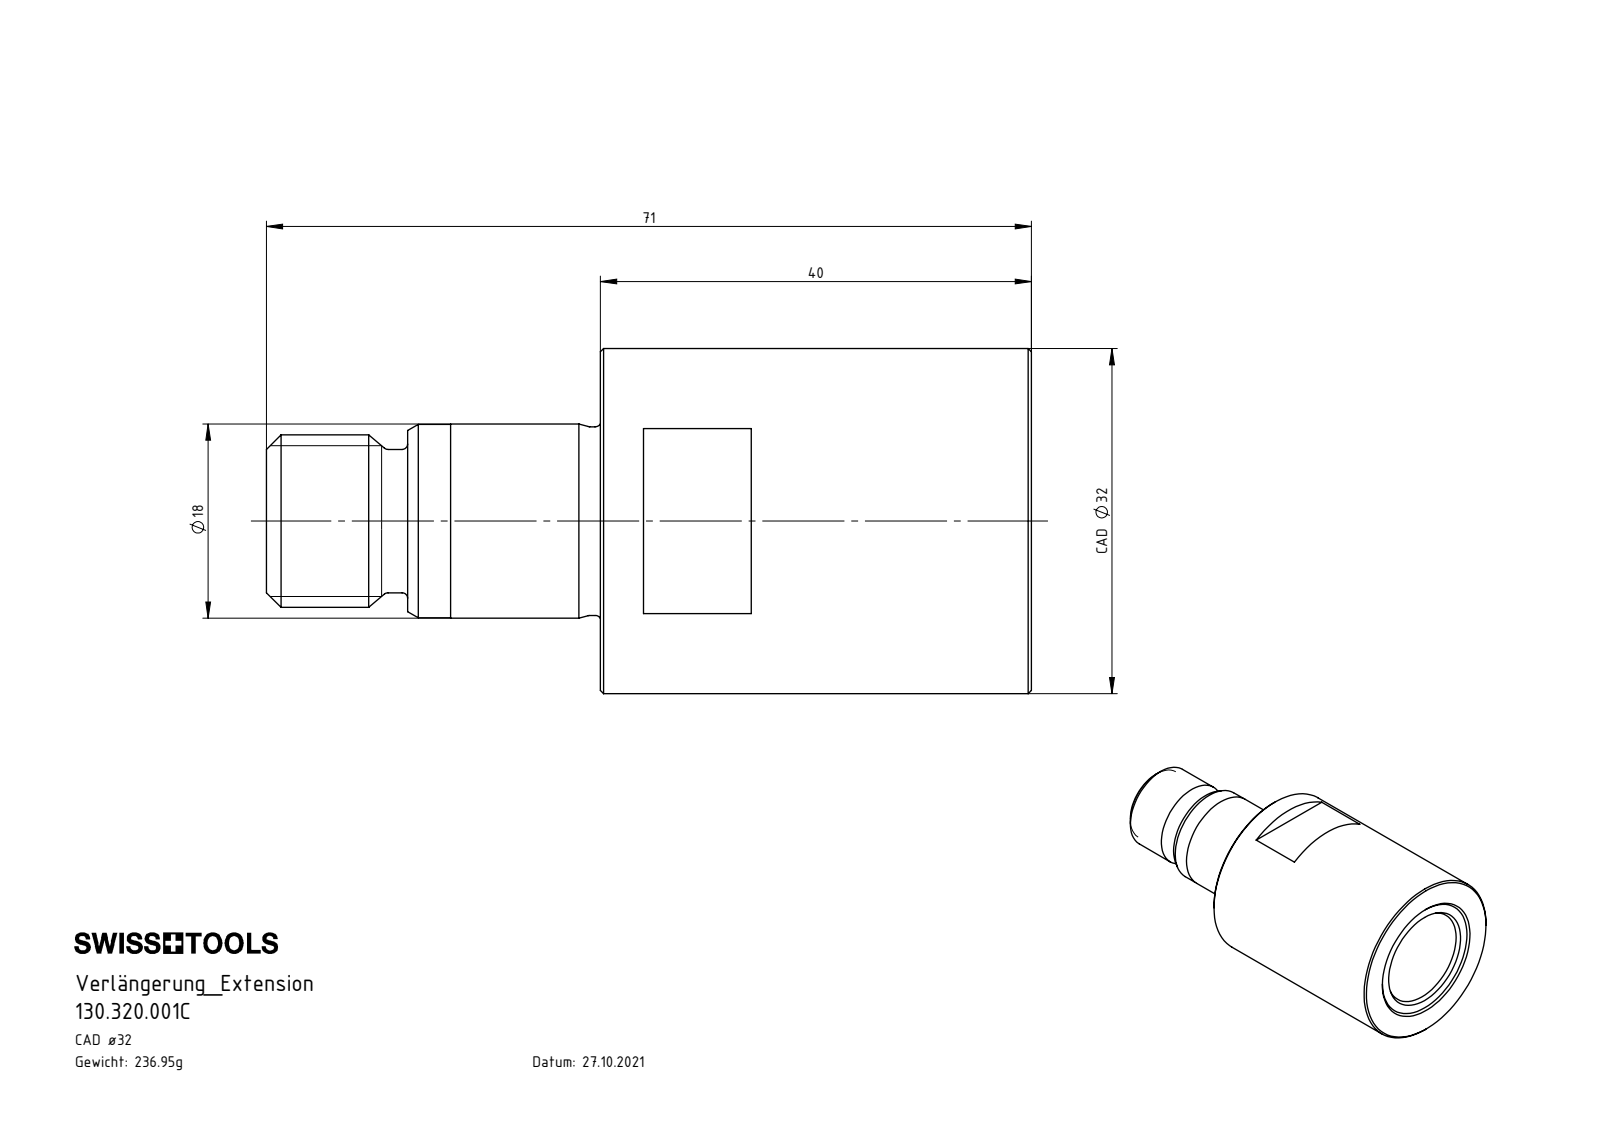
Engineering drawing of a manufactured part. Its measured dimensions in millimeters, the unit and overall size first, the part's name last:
Units: millimetres
Overall size (bounding box): 71 × 32 × 32
Round holes (diameter × count): ⌀4.2 ×1, ⌀14 ×1, ⌀18 ×1, ⌀18.5 ×1
Round bosses / shafts (diameter × count): ⌀32 ×1, ⌀17.95 ×1, ⌀17.5 ×1, ⌀16 ×1, ⌀13.3 ×1
Main face-to-face distances: 40, 27, 31, 71, 70.6, 39.6, 0.4, 17.9, 13.1, 57.5
Volume: 30 185 mm³ · Surface area: 9 566 mm²
Bodies: 1 solid, 71 faces (13 planar, 20 cylindrical, 38 other)
Part name (STEP PRODUCT): 130.320.001C
STEP written by: SolidWorks 2022 (CONFIG_CONTROL_DESIGN)
